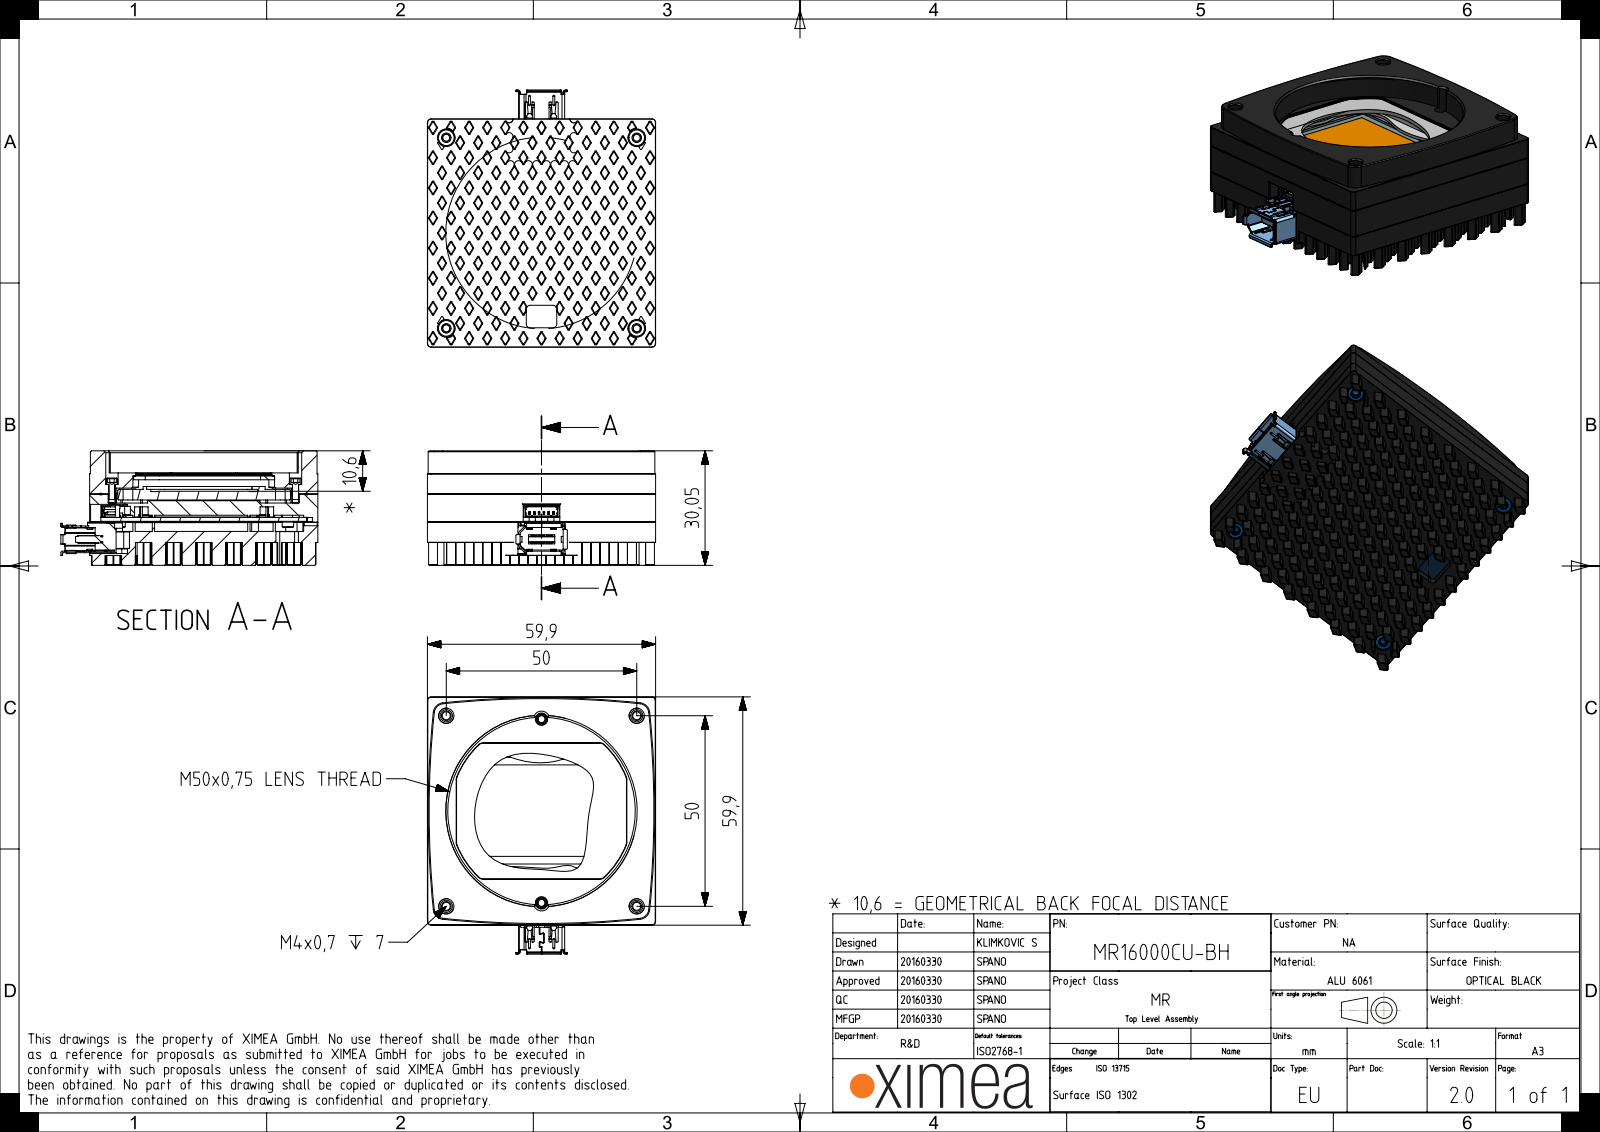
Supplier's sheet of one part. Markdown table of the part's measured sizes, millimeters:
| quantity | value |
| --- | --- |
| part name | SROB-M2.5X14-IMBUS-STNLS; SROB-M1.6X4-IMBUS-STNLS; SROB-M1.6X3-IMBUS-STNLS; IR_filter_24x36 (+8 more) |
| STEP written by | SIEMENS PLM Software NX 8.5 (AUTOMOTIVE_DESIGN) |
| units | millimeters |
| bodies | 18 solids, 5827 faces (3032 planar, 1482 cylindrical, 1313 other) |
| overall size | 67.45 × 59.9 × 30.05 |
| volume | 62 662 mm³ |
| surface area | 53 909 mm² |
| round holes (diameter × count) | 1.6 × 41, 0.95 × 40, 0.5 × 32, 1.8 × 10, 2.1 × 10, 2.5 × 10, 0.8 × 4, 1.3 × 4, 3.2 × 4, 4.62 × 4, 2.54 × 3, 1.5 × 2 |
| round bosses / shafts (diameter × count) | 0.46 × 40, 3 × 6, 4.5 × 4, 2.04 × 4, 1.6 × 4 |
| partial cylindrical surfaces (radius × count) | 0.2 × 702, 0.25 × 76, 1 × 50, 1.5 × 50, 0.3 × 48, 0.5 × 40, 0.15 × 12, 0.55 × 8 |
| main face-to-face distances | 5.55, 7.15, 4.07, 8.14, 12.7, 6.1, 11.35, 5.35, 6.58, 7.35 |
| hole center spacings | 33.15, 33.29, 1.78, 33.53, 33.86, 5.33, 7.11, 8.89 |
